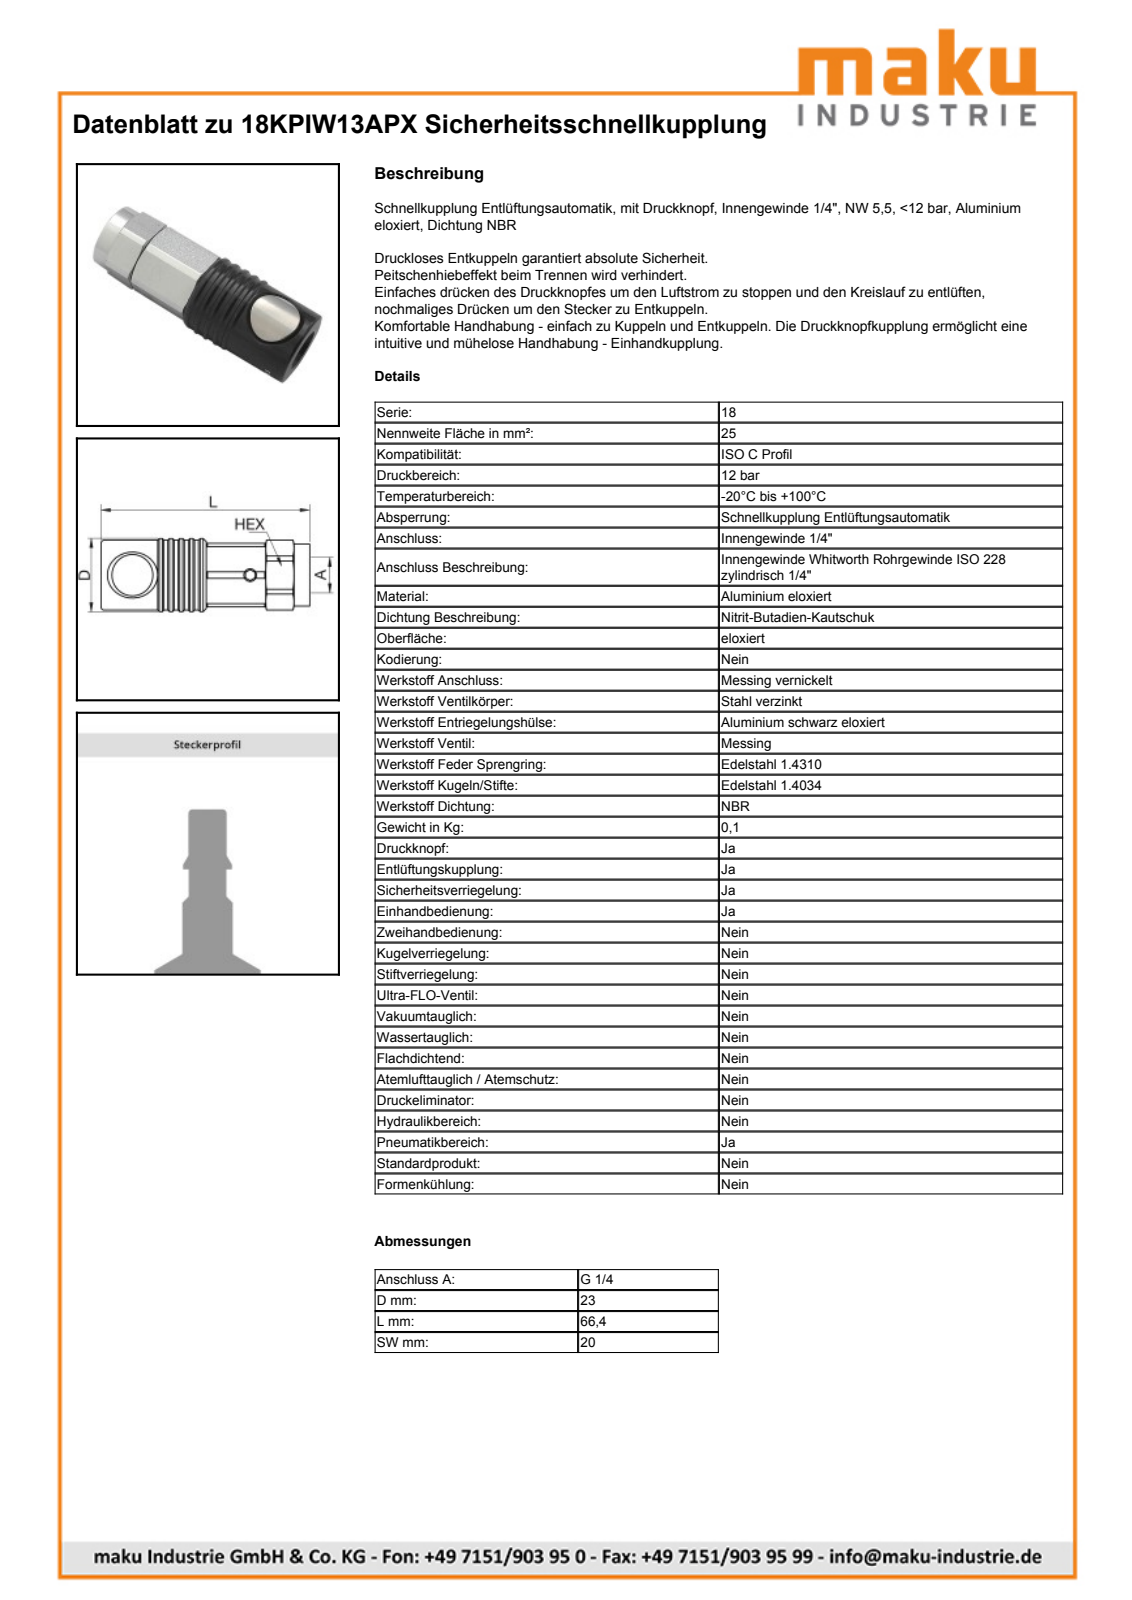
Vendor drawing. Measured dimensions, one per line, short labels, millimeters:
name: 18KPIW13APX
written by: Autodesk Inventor 2019 (CONFIG_CONTROL_DESIGN)
unit: mm
bodies: 27 solids, 296 faces (94 planar, 104 cylindrical, 98 other)
size: 66.4 × 23 × 23
volume: 27 526 mm³; area: 19 087 mm²
holes: 1× ⌀2.5, 1× ⌀3.5, 1× ⌀5.5, 1× ⌀7, 1× ⌀8.5, 1× ⌀10.1, 1× ⌀10.4, 1× ⌀10.5, 1× ⌀11.1, 1× ⌀11.41, 1× ⌀12.9, 1× ⌀14.05
bosses: 1× ⌀23, 1× ⌀22, 1× ⌀20, 1× ⌀19.5, 1× ⌀18.5, 1× ⌀18.2, 1× ⌀18, 1× ⌀15.8
rounds: 1× R3.77, 1× R7.22, 1× R7.8, 1× R11, 1× R12.36
face distances: 20, 29.4, 23, 52.4, 11, 19, 4.5, 7, 0.31, 29.71
hole spacings: 1.2, 1.25, 37.43
